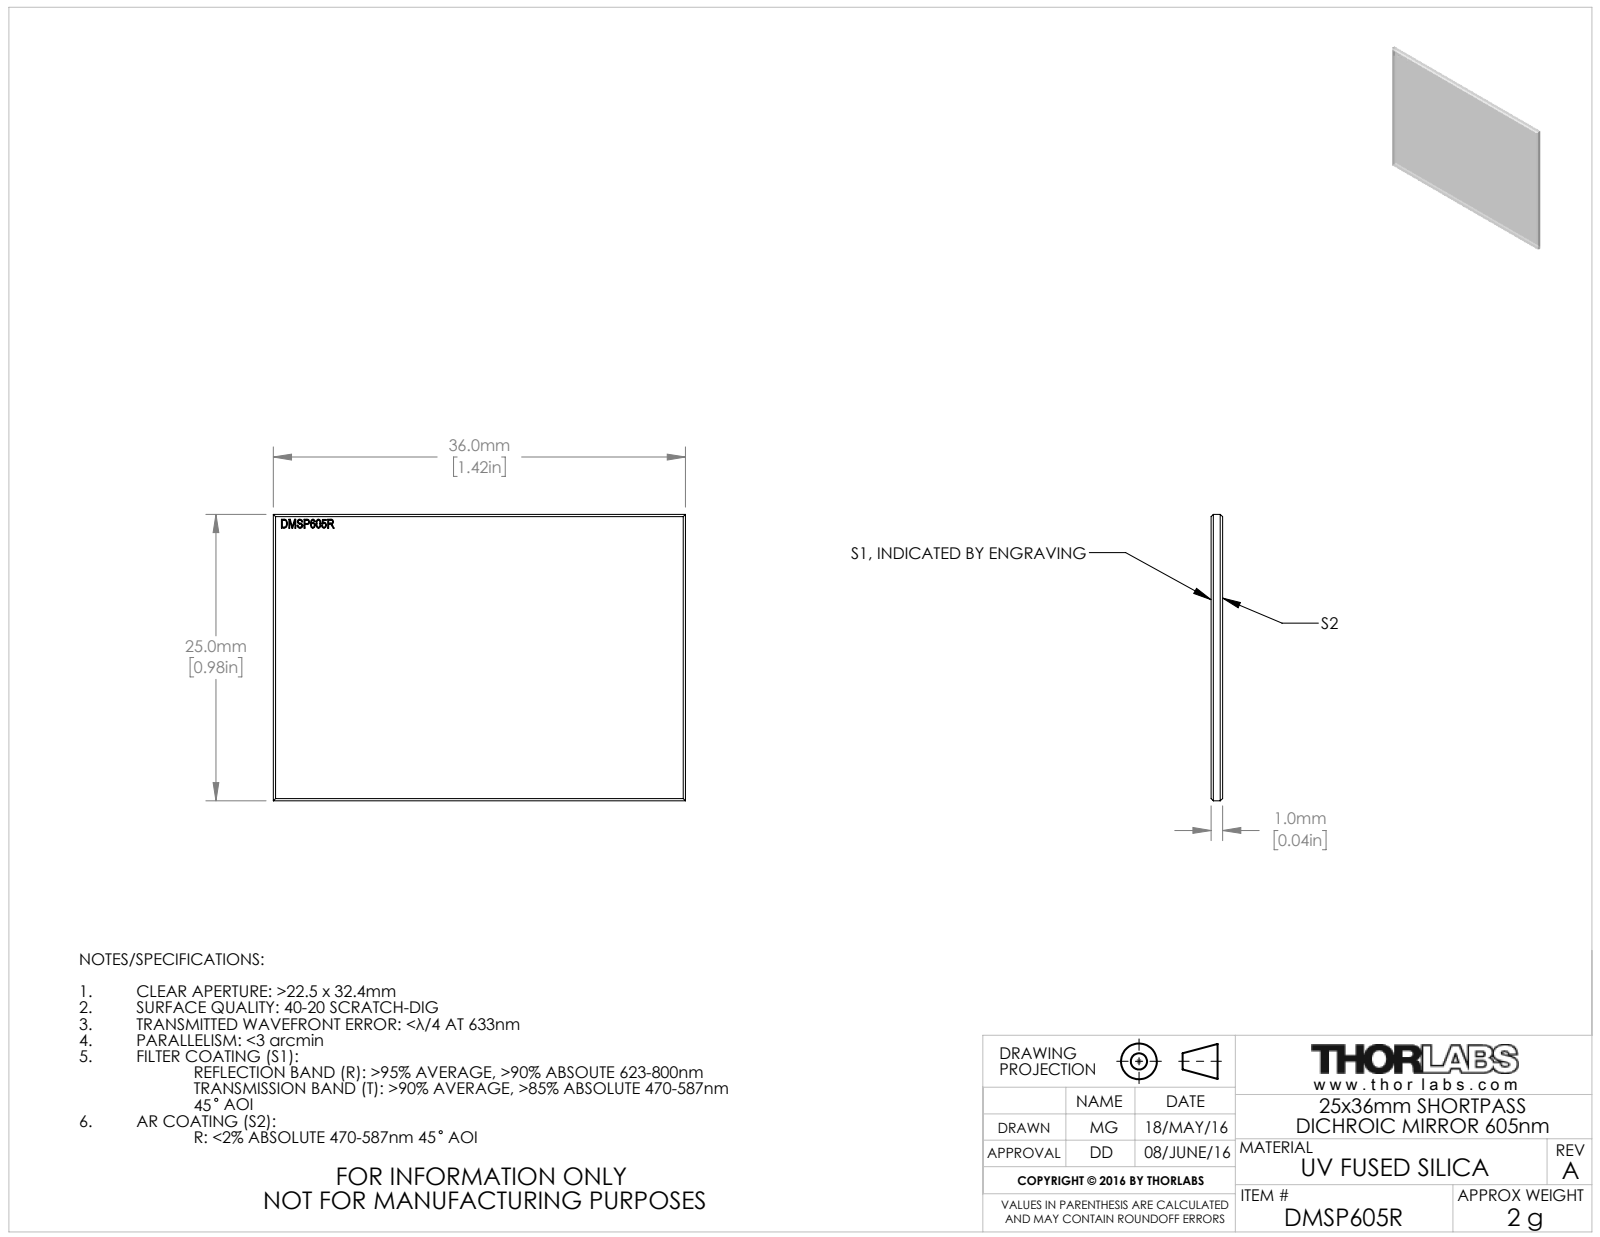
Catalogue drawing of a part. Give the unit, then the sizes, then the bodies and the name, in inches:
Units: inches
Overall size (bounding box): 1.417 × 0.984 × 0.039
Main face-to-face distances: 0.039, 0.984, 0.713, 1.417, 1.019, 0.039, 0.028, 0.078, 0.031, 0.021
Volume: 0.055 in³ · Surface area: 2.936 in²
Bodies: 1 solid, 141 faces (76 planar, 0 cylindrical, 65 other)
Part name (STEP PRODUCT): TTN045181-E0W
STEP written by: SolidWorks 2016 (CONFIG_CONTROL_DESIGN)
